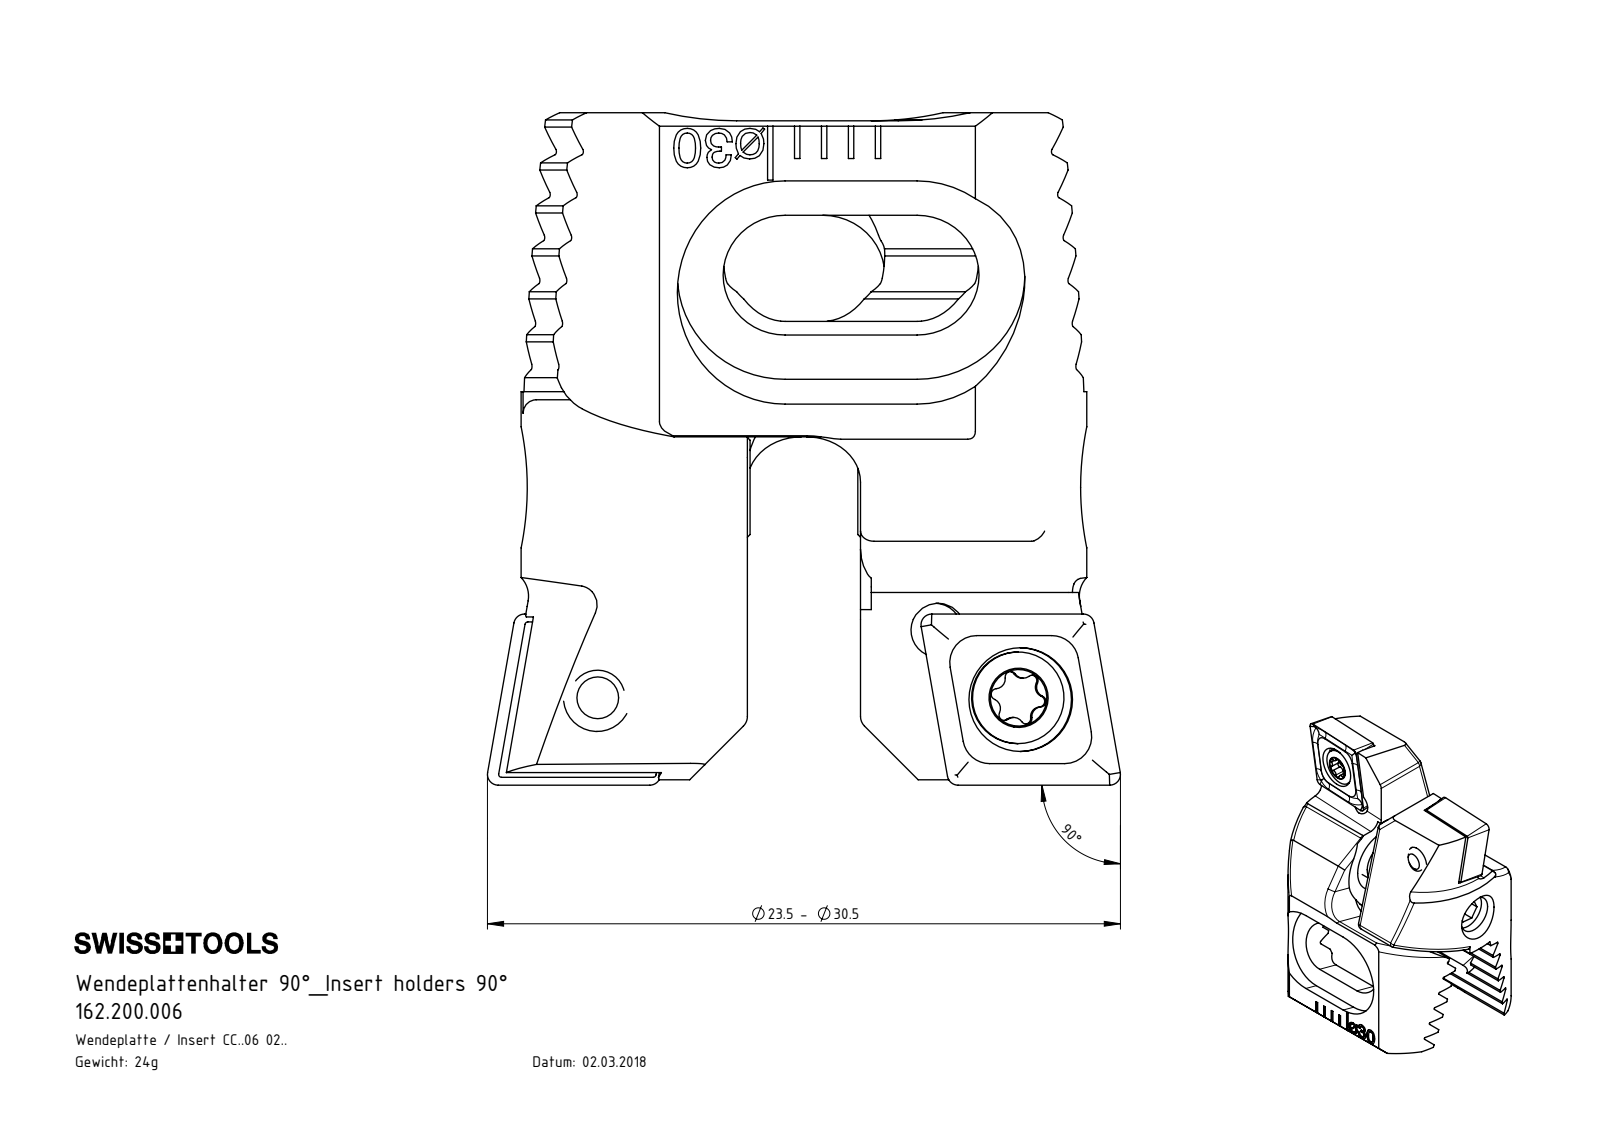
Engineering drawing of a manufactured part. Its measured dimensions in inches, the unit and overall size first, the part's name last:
Units: inches
Overall size (bounding box): 0.982 × 0.925 × 0.638
Round holes (diameter × count): ⌀0.063 ×2, ⌀0.079 ×2, ⌀0.081 ×2, ⌀0.11 ×2, ⌀0.152 ×2, ⌀0.138 ×1, ⌀0.358 ×1
Round bosses / shafts (diameter × count): ⌀0.134 ×2, ⌀0.098 ×2, ⌀0.157 ×1
Partial cylindrical surfaces — rounded edges, fillets, slot ends (radius × count): R0.02 ×16, R0.005 ×12, R0.008 ×12, R0.014 ×10, R0.039 ×4, R0.079 ×4, R0.091 ×4, R0.157 ×4
Main face-to-face distances: 0.056, 0.113, 0.169, 0.149, 0.016, 0.181, 0.225, 0.225, 0.117, 0.266
Hole centre spacings: 0.154, 0.158, 0.217, 0.518, 0.521, 0.629, 0.39, 0.418
Volume: 0.181 in³ · Surface area: 5.29 in²
Bodies: 8 solids, 606 faces (262 planar, 134 cylindrical, 210 other)
Part name (STEP PRODUCT): WCA-ER2.001.006_A; 162.200.006; Z20-xxx.001.015_D; Z20-ER3.001.007_A (+1 more)
STEP written by: SolidWorks 2017 (CONFIG_CONTROL_DESIGN)
